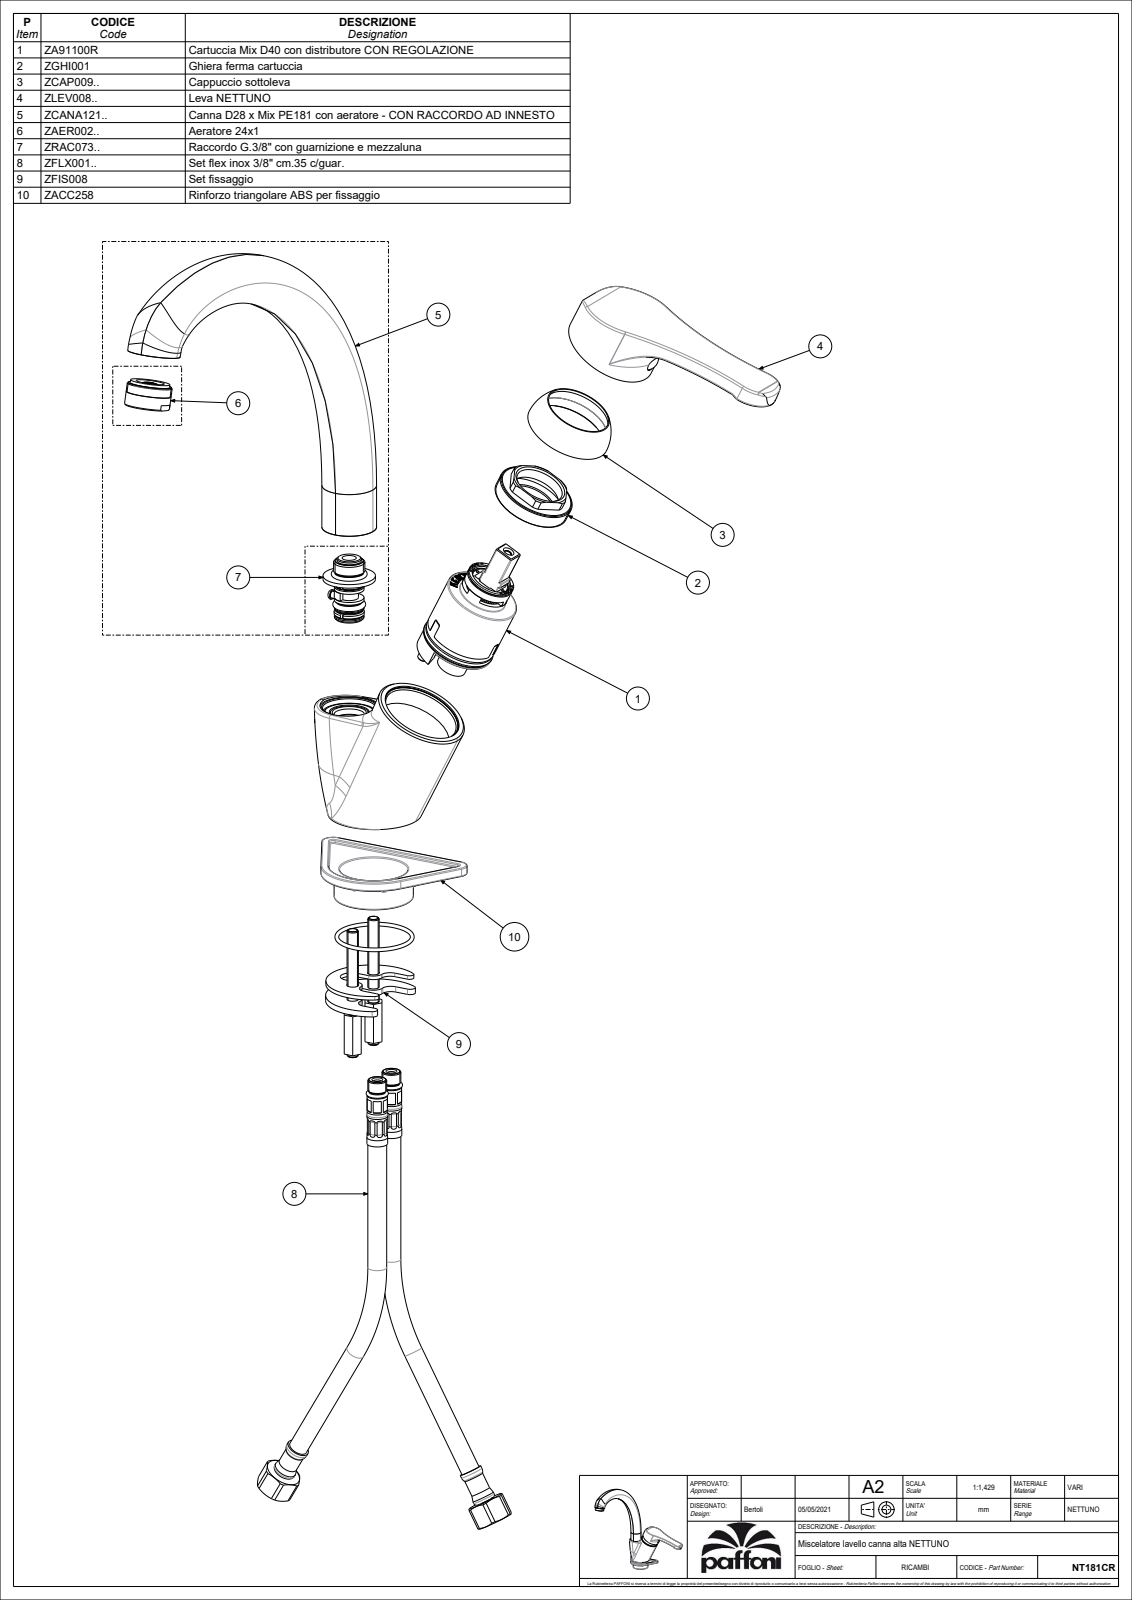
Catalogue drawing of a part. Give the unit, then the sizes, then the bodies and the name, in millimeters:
Units: millimetres
Overall size (bounding box): 251.6 × 245.52 × 168.19
Round holes (diameter × count): ⌀8 ×5, ⌀5 ×3, ⌀11 ×3, ⌀6 ×2, ⌀9 ×2, ⌀12 ×2, ⌀16 ×2, ⌀17 ×2, ⌀21 ×2, ⌀3.3 ×1, ⌀4 ×1, ⌀4.5 ×1
Round bosses / shafts (diameter × count): ⌀15.9 ×2, ⌀9.4 ×2, ⌀50 ×1, ⌀39.5 ×1, ⌀39.2 ×1, ⌀38.8 ×1, ⌀37 ×1, ⌀36.7 ×1
Partial cylindrical surfaces — rounded edges, fillets, slot ends (radius × count): R0.5 ×51, R0.2 ×24, R1.5 ×6, R1 ×5, R0.3 ×4, R2 ×4, R5.5 ×2, R7.5 ×2
Main face-to-face distances: 3, 1, 8, 5, 1.5, 2.5, 0.5, 9, 4, 10
Hole centre spacings: 9.9, 2, 8.6, 8.72, 9.92, 10.04, 12.78, 13.04
Volume: 205 024 mm³ · Surface area: 132 907 mm²
Bodies: 2 solids, 2813 faces (2022 planar, 407 cylindrical, 384 other)
Part name (STEP PRODUCT): NT181CR
STEP written by: CREO PARAMETRIC BY PTC INC, 2020044 (CONFIG_CONTROL_DESIGN)
